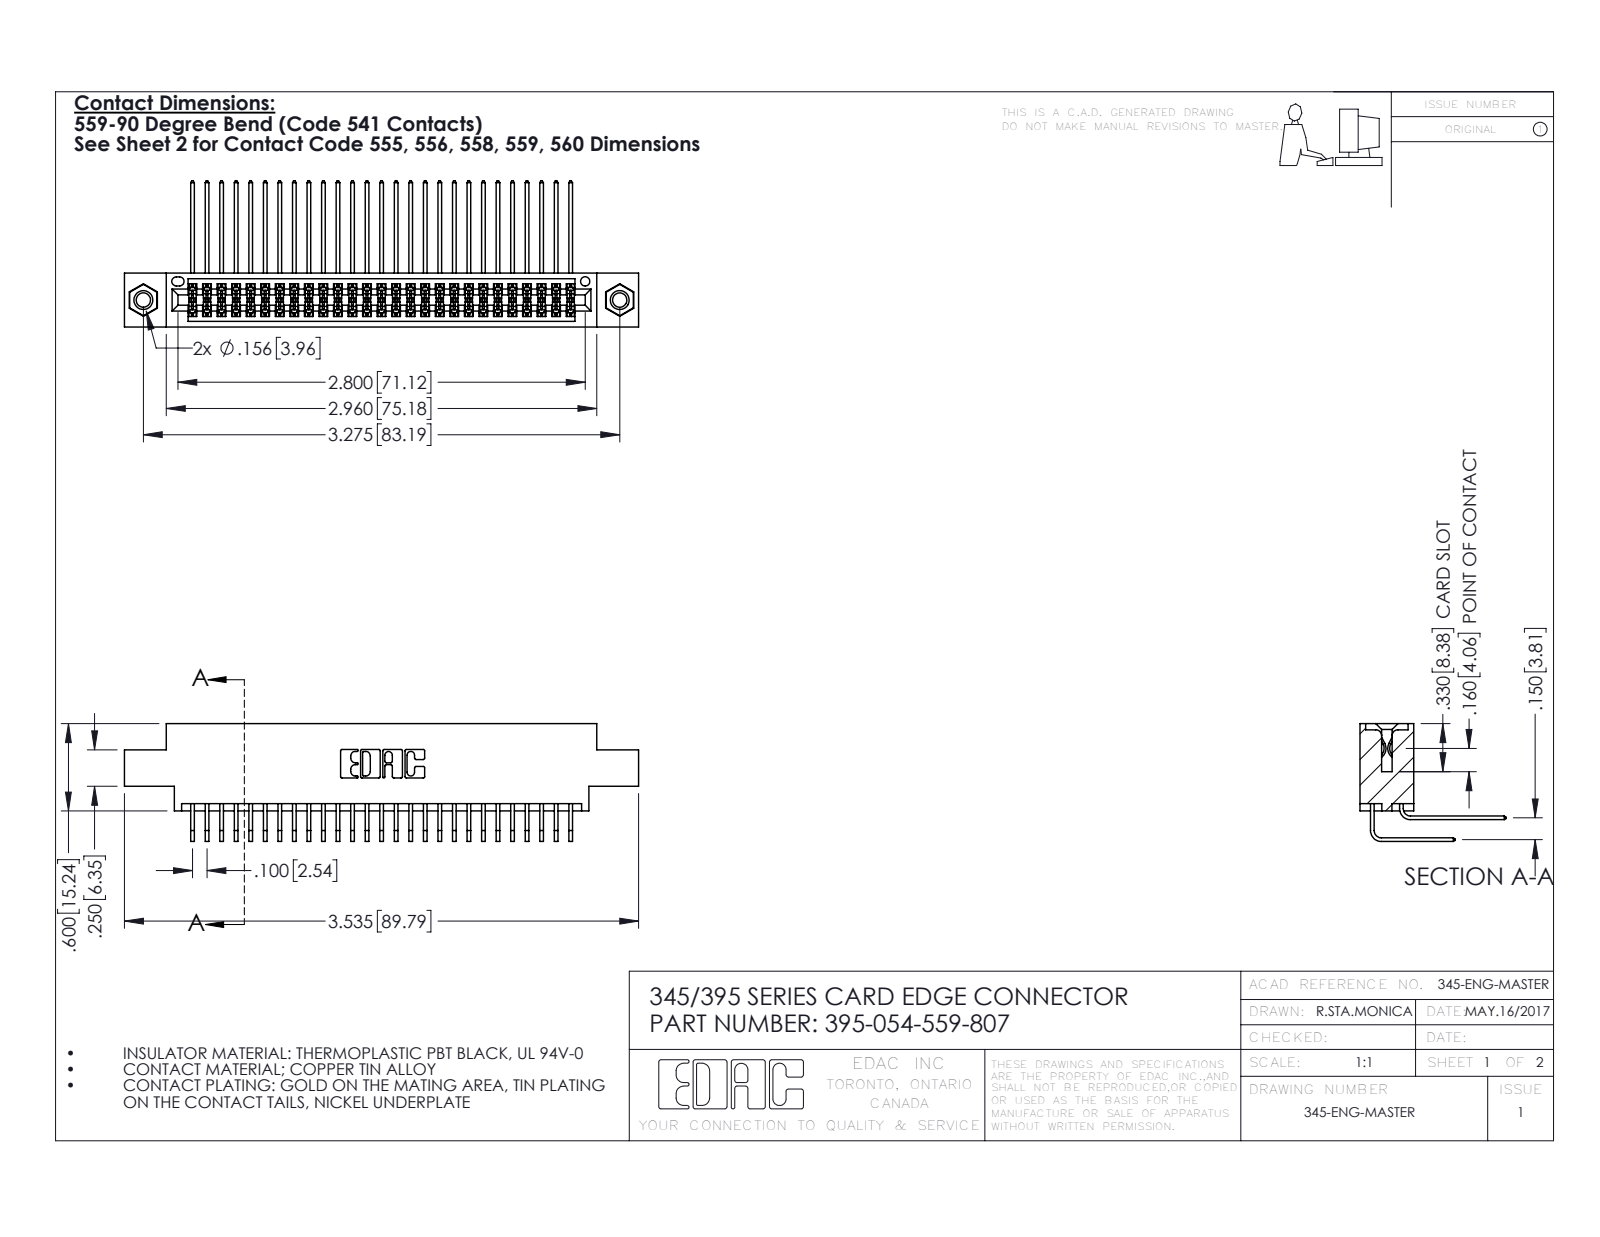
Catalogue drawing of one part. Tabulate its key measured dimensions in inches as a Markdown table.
| quantity | value |
| --- | --- |
| part name | 345-250-001_345-250-005-103; 345-292-001_558 559 Tail - 1; 345-292-001_559 Tail - 2; 395-054-559-807 (+1 more) |
| STEP written by | SolidWorks 2016 (CONFIG_CONTROL_DESIGN) |
| units | inches |
| bodies | 57 solids, 2998 faces (2006 planar, 976 cylindrical, 16 other) |
| overall size | 3.535 × 1.005 × 0.809 |
| volume | 0.535 in³ |
| surface area | 22.17 in² |
| round holes (diameter × count) | 0.098 × 2, 0.125 × 2, 0.156 × 2, 0.064 × 1 |
| round bosses / shafts (diameter × count) | 0.155 × 2 |
| partial cylindrical surfaces (radius × count) | 0.006 × 81, 0.01 × 22, 0.007 × 6, 0.031 × 6, 0.026 × 3, 0.014 × 2, 0.019 × 2, 0.022 × 2 |
| main face-to-face distances | 0.072, 0.298, 0.37, 0.2, 0.098, 0.272, 0.025, 0.225, 0.175, 0.15 |
| hole center spacings | 0.27, 3.04, 3.275 |
